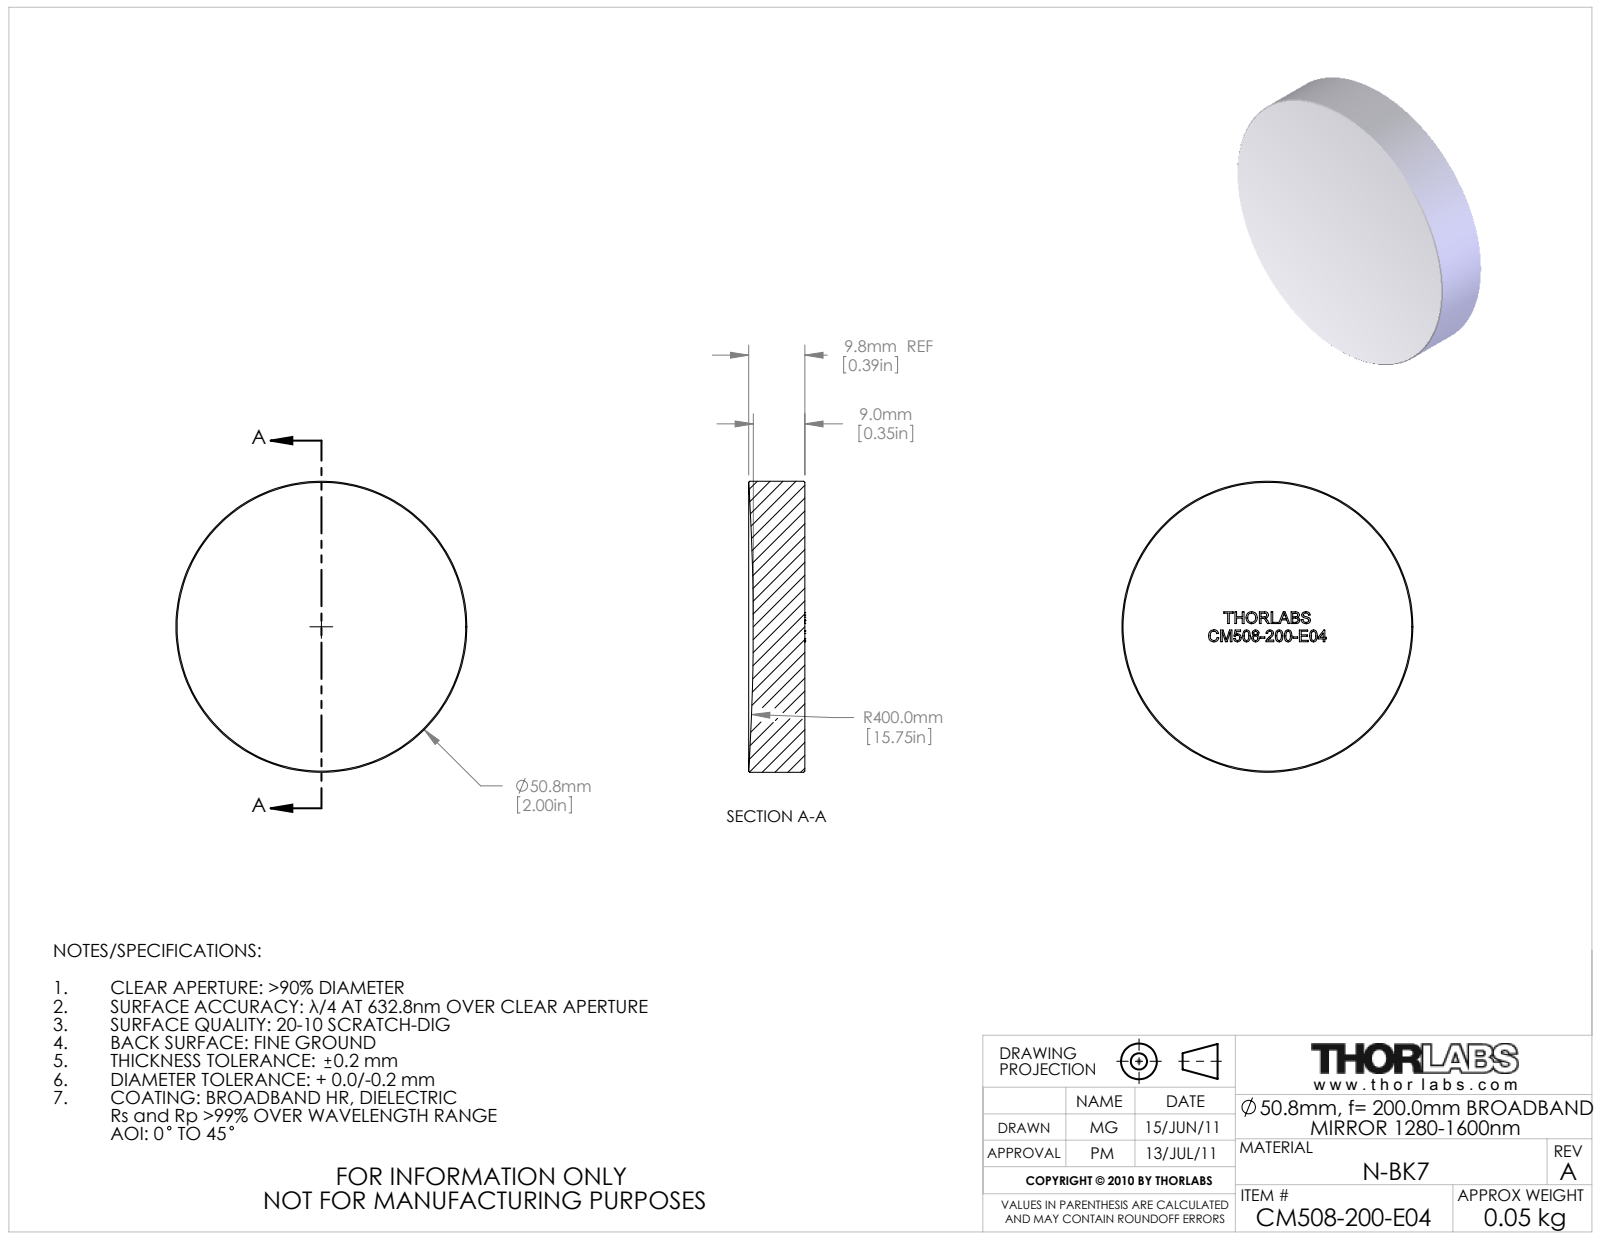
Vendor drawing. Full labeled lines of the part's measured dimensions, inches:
Part name (STEP PRODUCT): 22663-E0W
STEP written by: SolidWorks 2011 (AUTOMOTIVE_DESIGN)
Units: inches
Bodies: 0 solids, 44 faces (34 planar, 2 cylindrical, 8 other)
Overall size (bounding box): 2 × 2 × 0.385
Round bosses / shafts (diameter × count): ⌀2 ×1
